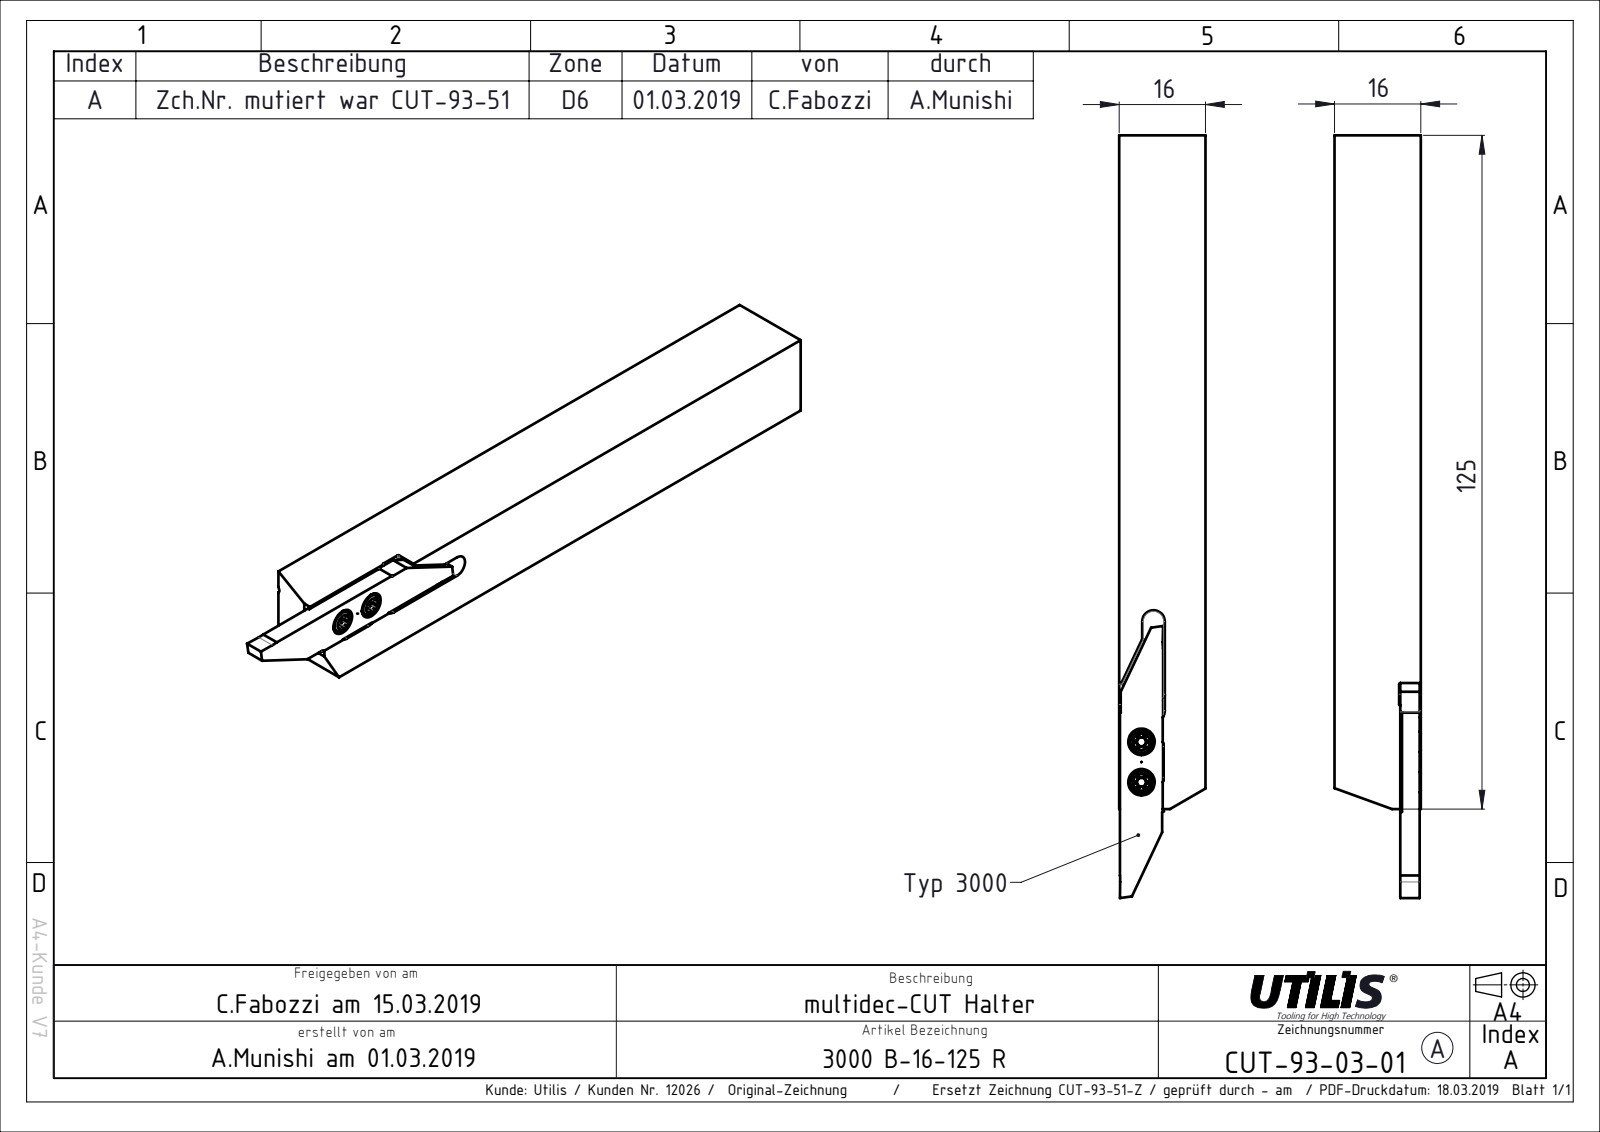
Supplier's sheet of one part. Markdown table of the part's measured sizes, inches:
| quantity | value |
| --- | --- |
| part name | CUT-Vorlage 3000 R+L Lang Kunde; CUT-93-Kunde; CUT-93-51; CUT-Vorlage 3000 R+L Lang Kunde_R-Lang (+1 more) |
| STEP written by | SolidWorks 2015 (CONFIG_CONTROL_DESIGN) |
| units | inches |
| bodies | 2 solids, 55 faces (36 planar, 19 cylindrical, 0 other) |
| overall size | 5.571 × 0.63 × 0.63 |
| volume | 1.921 in³ |
| surface area | 15.04 in² |
| round holes (diameter × count) | 0.098 × 2, 0.193 × 2 |
| partial cylindrical surfaces (radius × count) | 0.083 × 4, 0.006 × 2, 0.394 × 2 |
| main face-to-face distances | 0.63, 0.15, 0.48, 0.142, 0.622, 0.315, 0.297, 0.018, 0.333, 0.016 |
| hole center spacings | 0.148, 0.295 |
